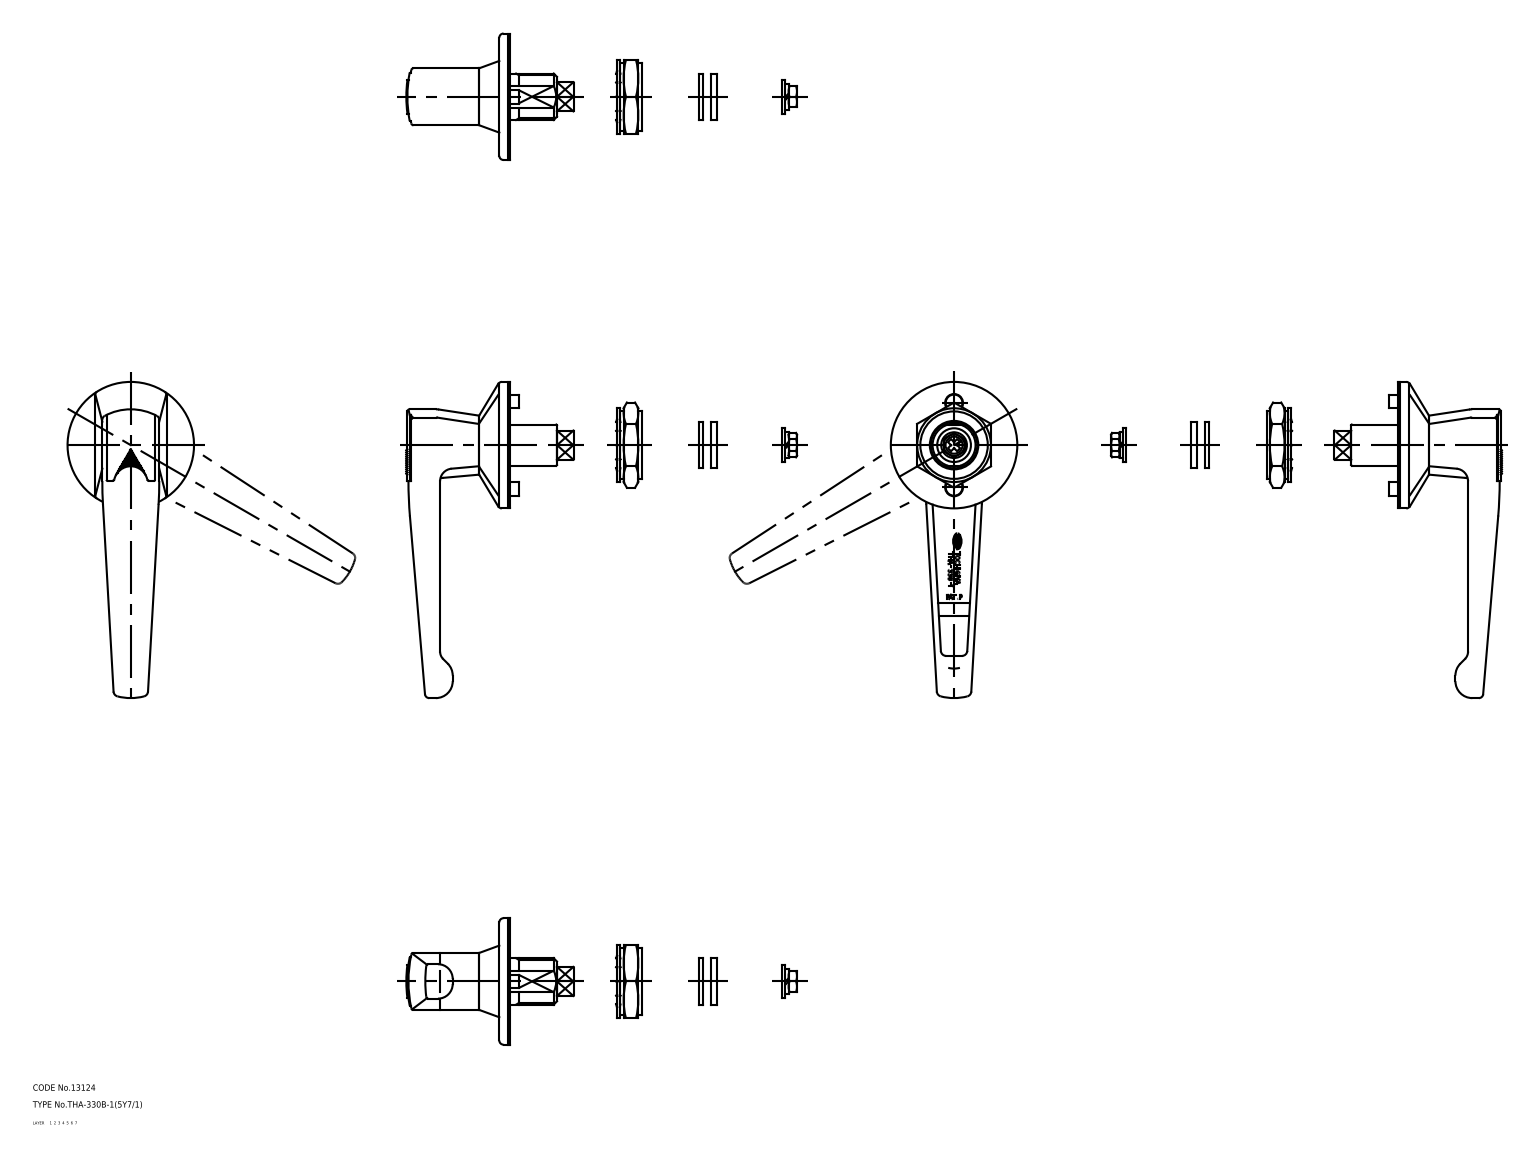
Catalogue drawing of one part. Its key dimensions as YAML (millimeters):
part_name: "washer_D; washer_C; washer_B; washer_A (+6 more)"
step_written_by: "CADfix (AUTOMOTIVE_DESIGN)"
units: millimeters
bodies: {solids: 9, faces: 307, planar: 0, cylindrical: 0, other: 307}
overall_size: [150, 86.6, 60]
volume: 84396
surface_area: 37986
